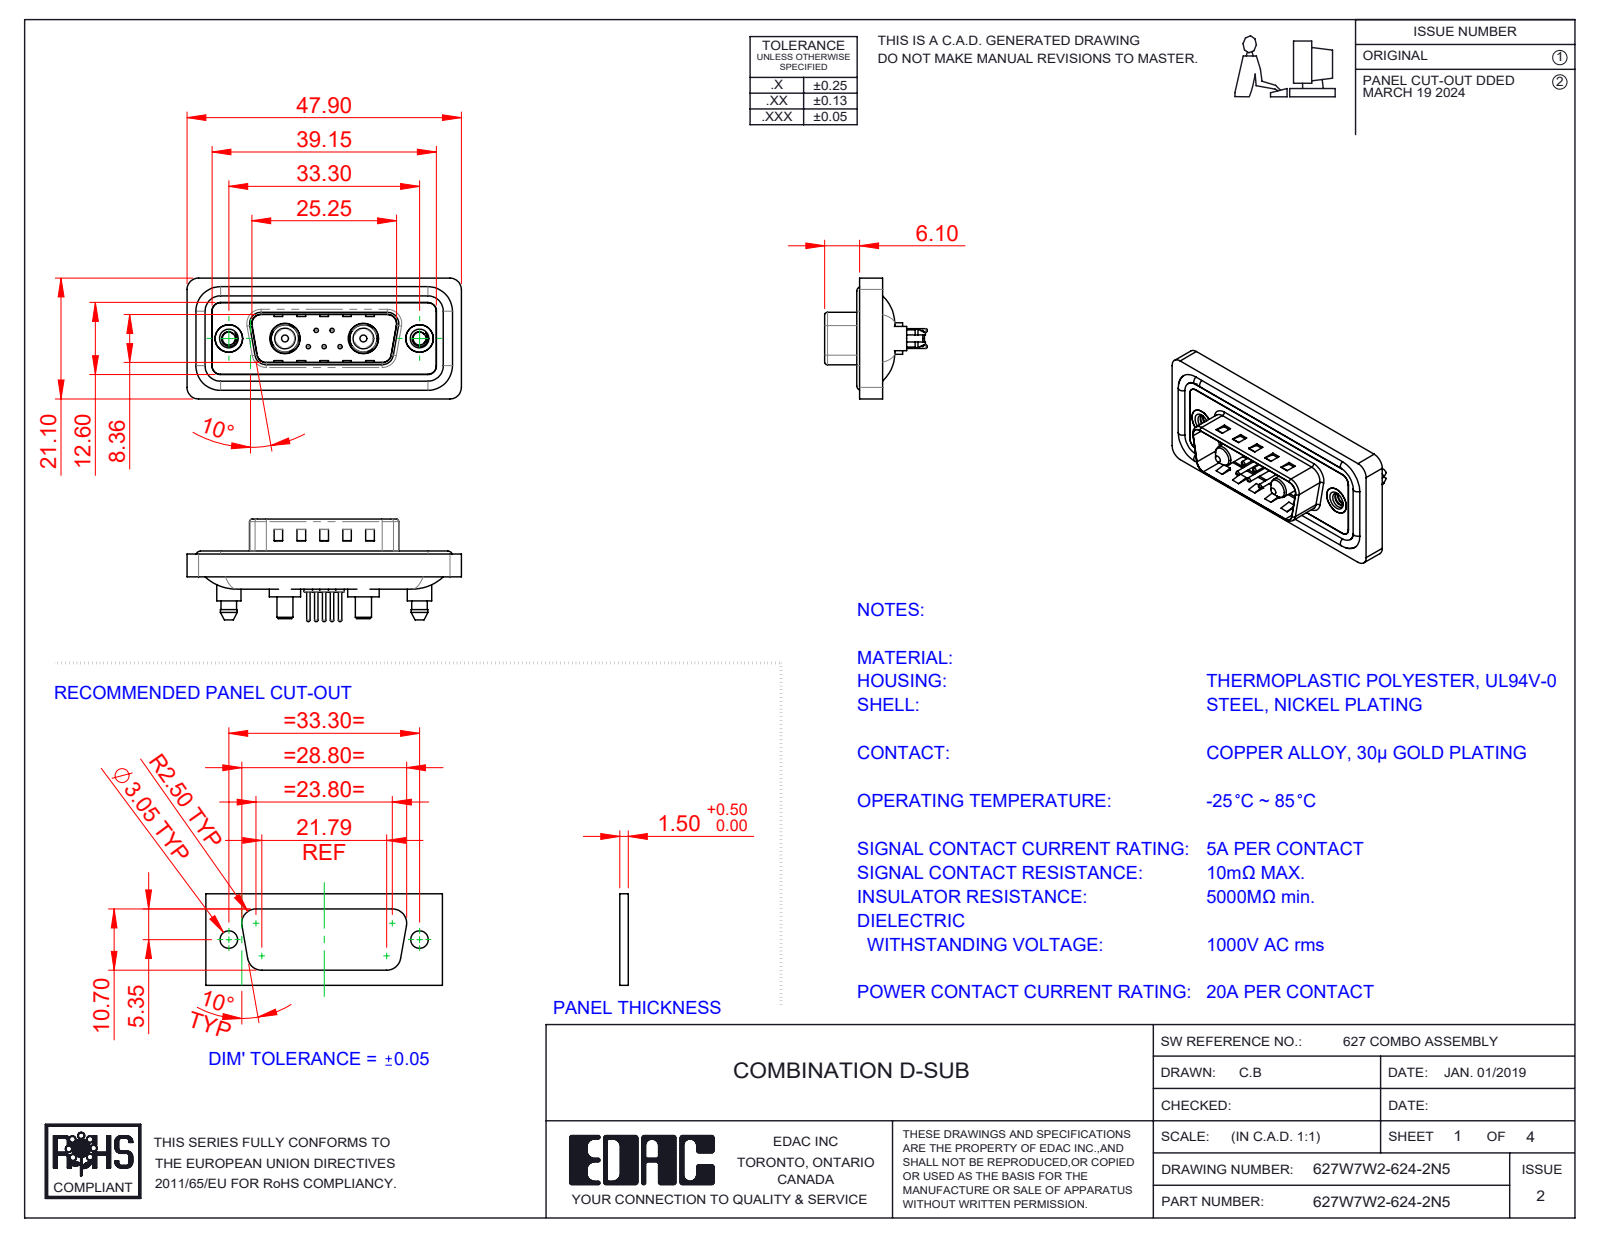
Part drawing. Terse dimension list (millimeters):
name: 627Combo Housing_7W2; 627Combo Shell Front_15 Contacts; Power Pin_20A S; 627Combo Shell Rear_15 Contacts (+5 more)
written by: SolidWorks 2023 (CONFIG_CONTROL_DESIGN)
unit: mm
bodies: 16 solids, 760 faces (248 planar, 324 cylindrical, 188 other)
size: 47.9 × 21.1 × 17.9
volume: 5 650 mm³; area: 9 126 mm²
holes: 5× ⌀0.75, 5× ⌀1.6, 5× ⌀2, 2× ⌀2.26, 2× ⌀4, 2× ⌀4.8, 2× ⌀4.85, 2× ⌀5, 2× ⌀5.3
bosses: 5× ⌀1.5, 5× ⌀0.6, 4× ⌀1.6, 2× ⌀5.5, 2× ⌀5.4, 2× ⌀5.2, 2× ⌀4.9, 2× ⌀4.75
rounds: 28× R1.5, 20× R2, 10× R1.6, 8× R0.5, 4× R0.25, 4× R0.6, 4× R0.65, 4× R0.9
face distances: 0.4, 1.1, 1.5, 1.6, 0.5, 3.1, 2.9, 4, 0.7, 0.82
hole spacings: 3.16, 2.77, 9.8, 23.5, 4.31, 4.33, 5.03, 5.04
